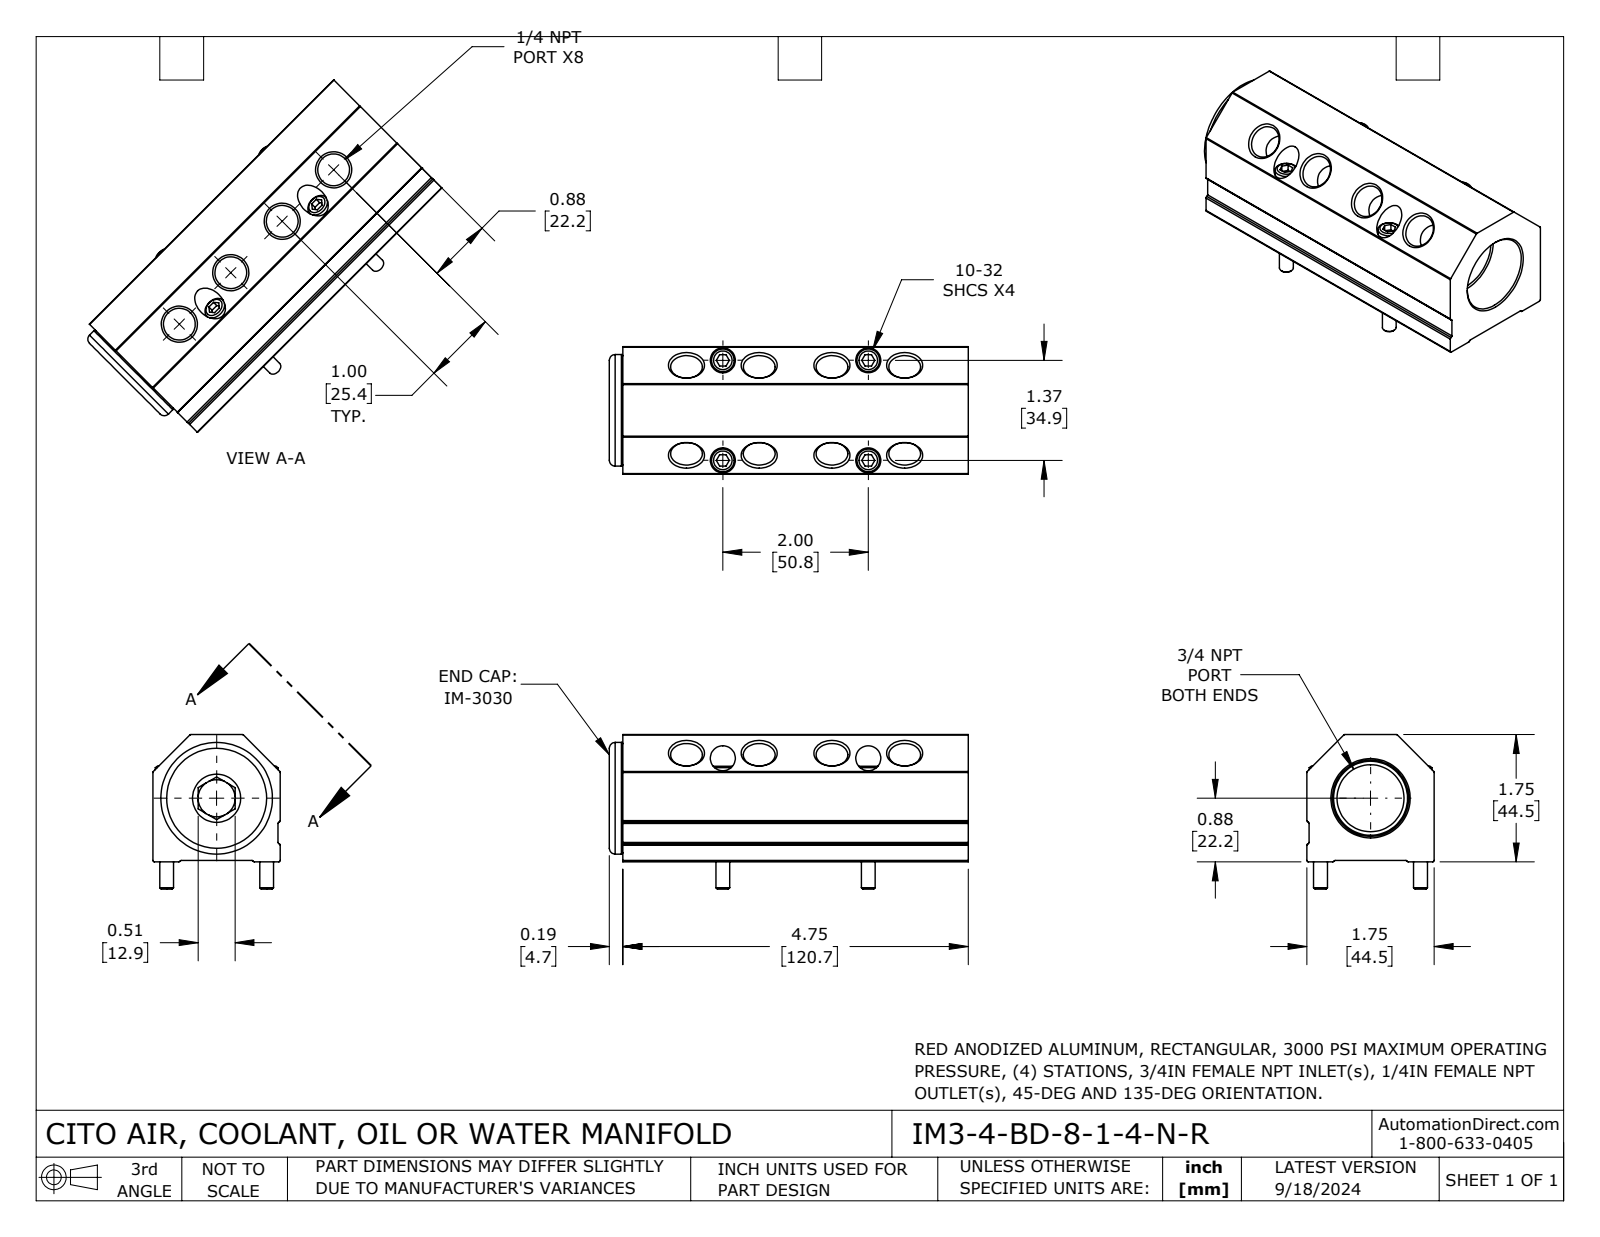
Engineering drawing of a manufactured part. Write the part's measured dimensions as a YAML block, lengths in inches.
part_name: "IM3-4-BD-8-1-4-N-R"
step_written_by: "SolidWorks 2023 (CONFIG_CONTROL_DESIGN)"
units: inches
bodies: {solids: 6, faces: 216, planar: 82, cylindrical: 74, other: 60}
overall_size: [4.935, 2.125, 1.75]
volume: 9.729
surface_area: 66.59
round_holes:
  - {diameter: 0.437, count: 8}
  - {diameter: 0.203, count: 4}
  - {diameter: 0.344, count: 4}
  - {diameter: 0.51, count: 1}
  - {diameter: 0.921, count: 1}
  - {diameter: 1.394, count: 1}
round_bosses_or_shafts:
  - {diameter: 0.312, count: 4}
  - {diameter: 0.19, count: 4}
  - {diameter: 1.534, count: 1}
  - {diameter: 1.182, count: 1}
  - {diameter: 0.938, count: 1}
partial_cylinders:
  - {radius: 0.02, count: 14}
face_to_face_distances: [1.75, 1.73, 0.02, 1.75, 4.75, 0.03, 1.72, 0.185, 4.935, 0.531]
hole_center_spacings: [1, 2, 1.375, 2.427, 3]
